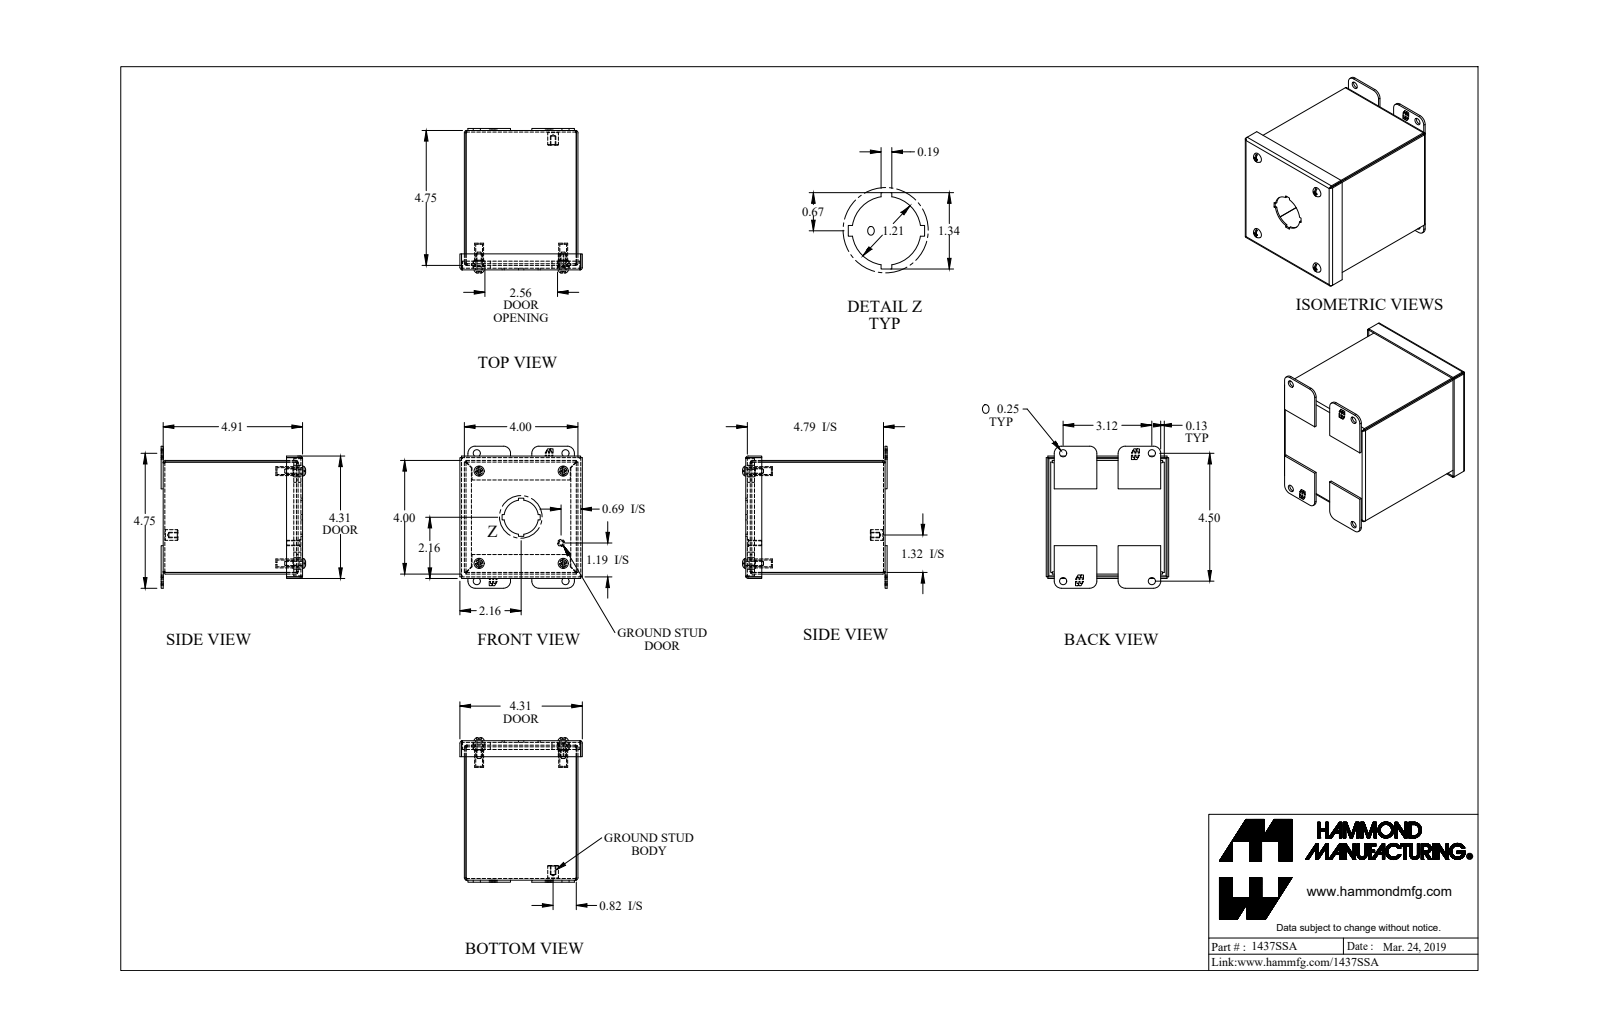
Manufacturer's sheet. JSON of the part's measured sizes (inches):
{"part_name": "1437SSA_Default", "step_written_by": "SolidWorks 2019 (CONFIG_CONTROL_DESIGN)", "units": "inches", "bodies": {"solids": 21, "faces": 541, "planar": 371, "cylindrical": 140, "other": 30}, "overall_size": [5.089, 5, 4.312], "volume_in3": 9.235, "surface_area_in2": 294.7, "round_holes": [[0.25, 8], [0.065, 4], [0.239, 4], [0.253, 4], [0.406, 4], [0.156, 1], [1.21, 1]], "round_bosses_or_shafts": [[0.19, 5], [0.406, 4], [0.315, 4], [0.148, 4], [0.375, 1], [0.25, 1]], "partial_cylinders_radius": [[0.029, 12], [0.086, 12], [0.25, 8], [0.171, 4], [0.125, 2]], "face_to_face_distances": [0.057, 3.943, 4.85, 3.886, 4, 4.907, 0.156, 4.099, 4.793, 0.157], "hole_center_spacings": [3.25, 0.63, 2.961, 3.107, 3.876, 4.396, 4.927, 2.962]}
